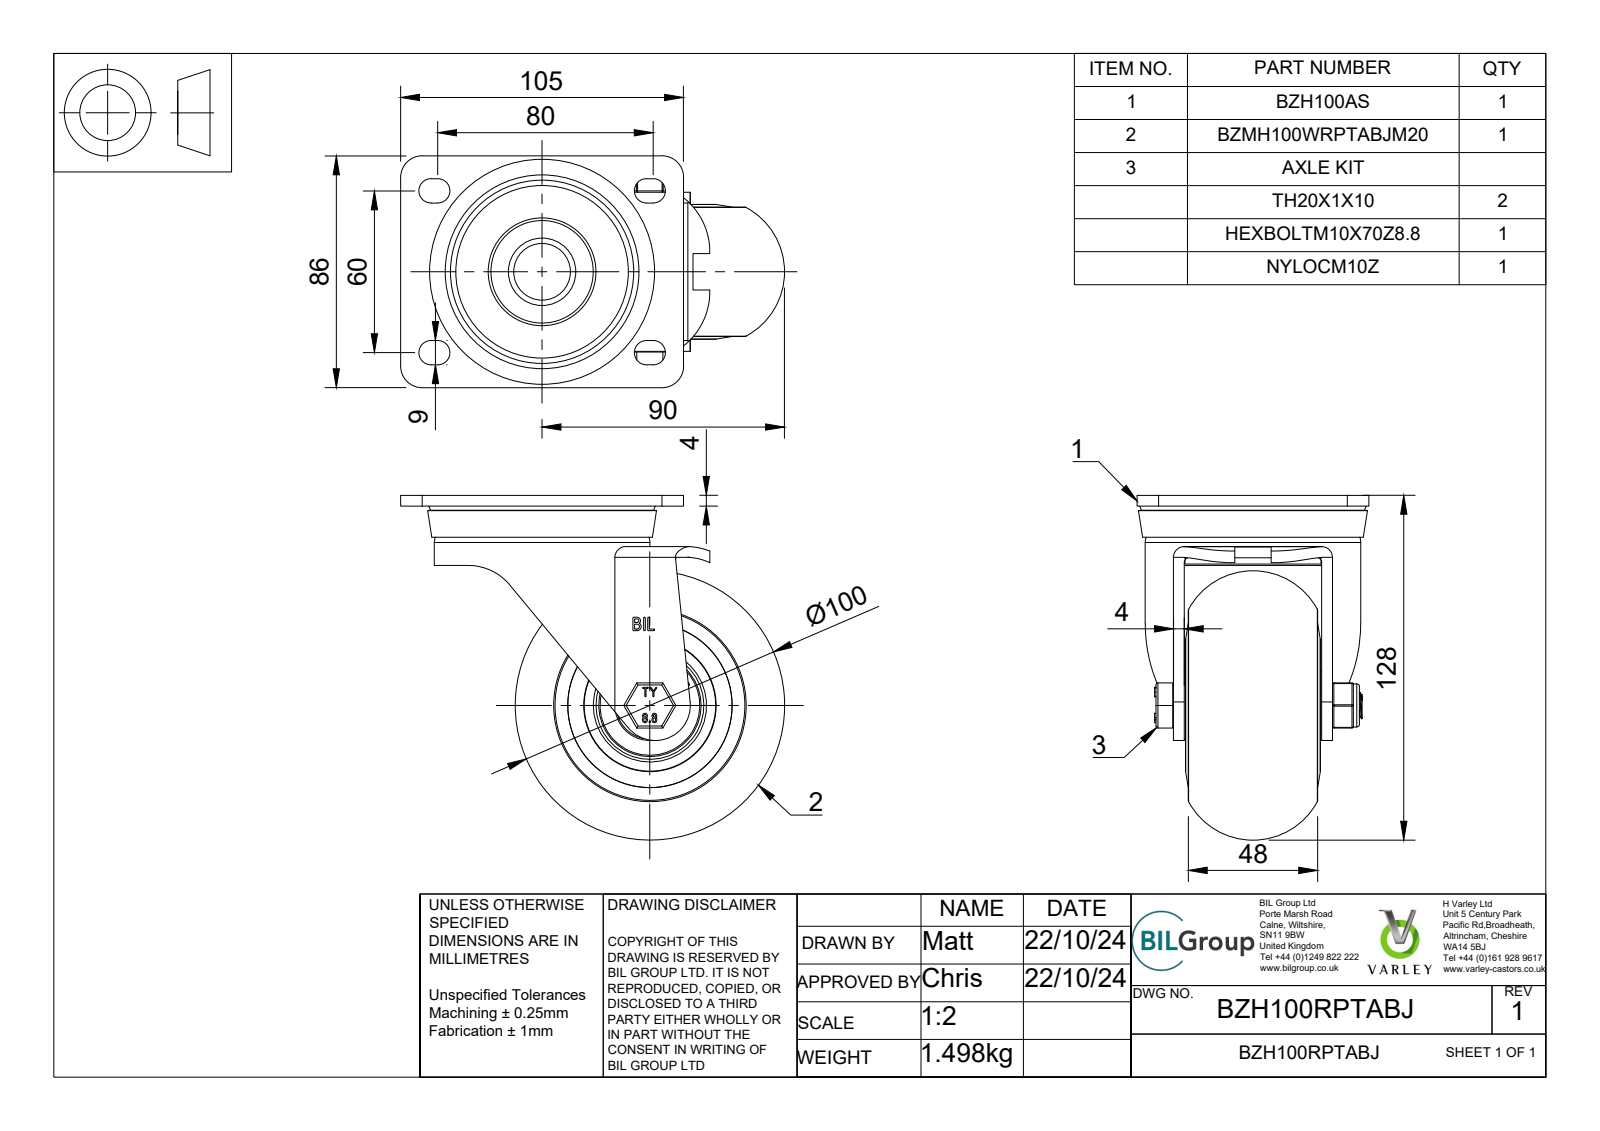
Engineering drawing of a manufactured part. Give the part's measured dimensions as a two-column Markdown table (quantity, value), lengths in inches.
| quantity | value |
| --- | --- |
| part name | BZH100RPTABJ v3; BZH100AS - 2 v1; ZINC PLATED, PRESSED STEEL TOP PLATE (1); ZINC PLATED, PRESSED STEEL FORKS (1) (+8 more) |
| STEP written by | Autodesk Translation Framework v13.20.0.188 (AUTOMOTIVE_DESIGN) |
| units | inches |
| bodies | 39 solids, 1268 faces (499 planar, 247 cylindrical, 522 other) |
| overall size | 5.61 × 5.039 × 3.386 |
| volume | 26.24 in³ |
| surface area | 247.9 in² |
| round holes (diameter × count) | 0.236 × 8, 0.394 × 1, 0.402 × 1, 0.413 × 1, 0.472 × 1, 0.787 × 1, 0.827 × 1, 0.984 × 1, 1.024 × 1, 1.26 × 1, 1.378 × 1, 1.417 × 1 |
| round bosses / shafts (diameter × count) | 0.315 × 18, 3.15 × 1, 1.988 × 1, 1.457 × 1, 1.22 × 1, 1.063 × 1, 0.984 × 1, 0.945 × 1 |
| partial cylindrical surfaces (radius × count) | 0.02 × 18, 0.177 × 8, 0.03 × 6, 0.079 × 4, 0.315 × 4, 0.157 × 2, 1 × 2, 0.513 × 1 |
| main face-to-face distances | 0.157, 1.004, 0.02, 0.846, 0.453, 0.295, 1.496, 0.315, 0.059, 0.039 |
| hole center spacings | 1.062, 2.565, 1.388, 1.388, 1.963, 1.963, 2.776, 2.776 |
